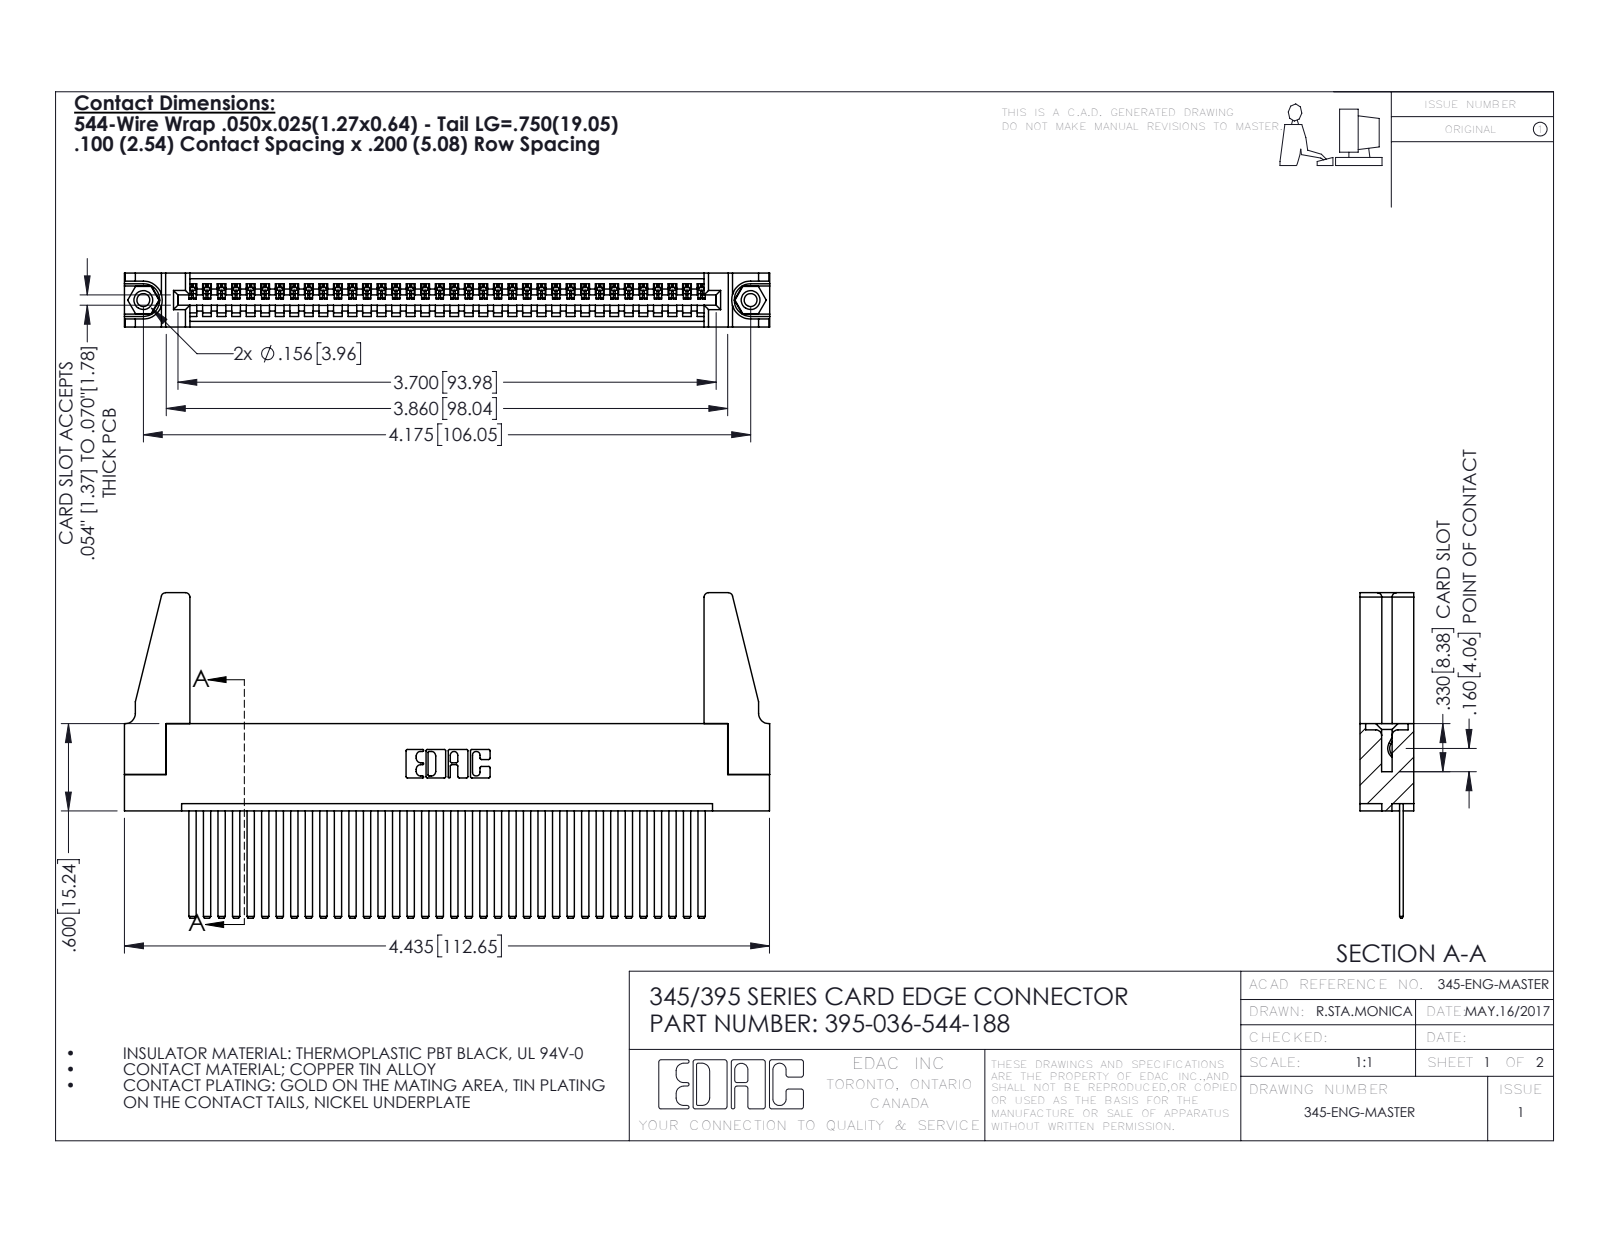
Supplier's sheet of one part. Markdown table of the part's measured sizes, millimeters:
| quantity | value |
| --- | --- |
| part name | 345 Part_Flush Mounting Lugs - 0.156 Dia-TH; 345-220-078_345-220-088; 345-250-001_345-250-001-102; 345-292-001_345-293-144 (+1 more) |
| STEP written by | SolidWorks 2016 (CONFIG_CONTROL_DESIGN) |
| units | millimeters |
| bodies | 41 solids, 2122 faces (1448 planar, 658 cylindrical, 16 other) |
| overall size | 112.7 × 56.8 × 9.4 |
| volume | 14 300 mm³ |
| surface area | 19 010 mm² |
| round holes (diameter × count) | 2.3 × 2, 3.2 × 2, 4 × 2, 1.6 × 1 |
| round bosses / shafts (diameter × count) | 3.9 × 2 |
| partial cylindrical surfaces (radius × count) | 0.2 × 72, 0.3 × 22, 0.8 × 8, 0.2 × 6, 0.8 × 6, 0.7 × 3, 0.8 × 2, 1 × 2 |
| main face-to-face distances | 1.8, 7.6, 2.5, 6.9, 0.6, 9.4, 5.1, 5.7, 3.8, 1.8 |
| hole center spacings | 6.9, 100.1, 106 |
